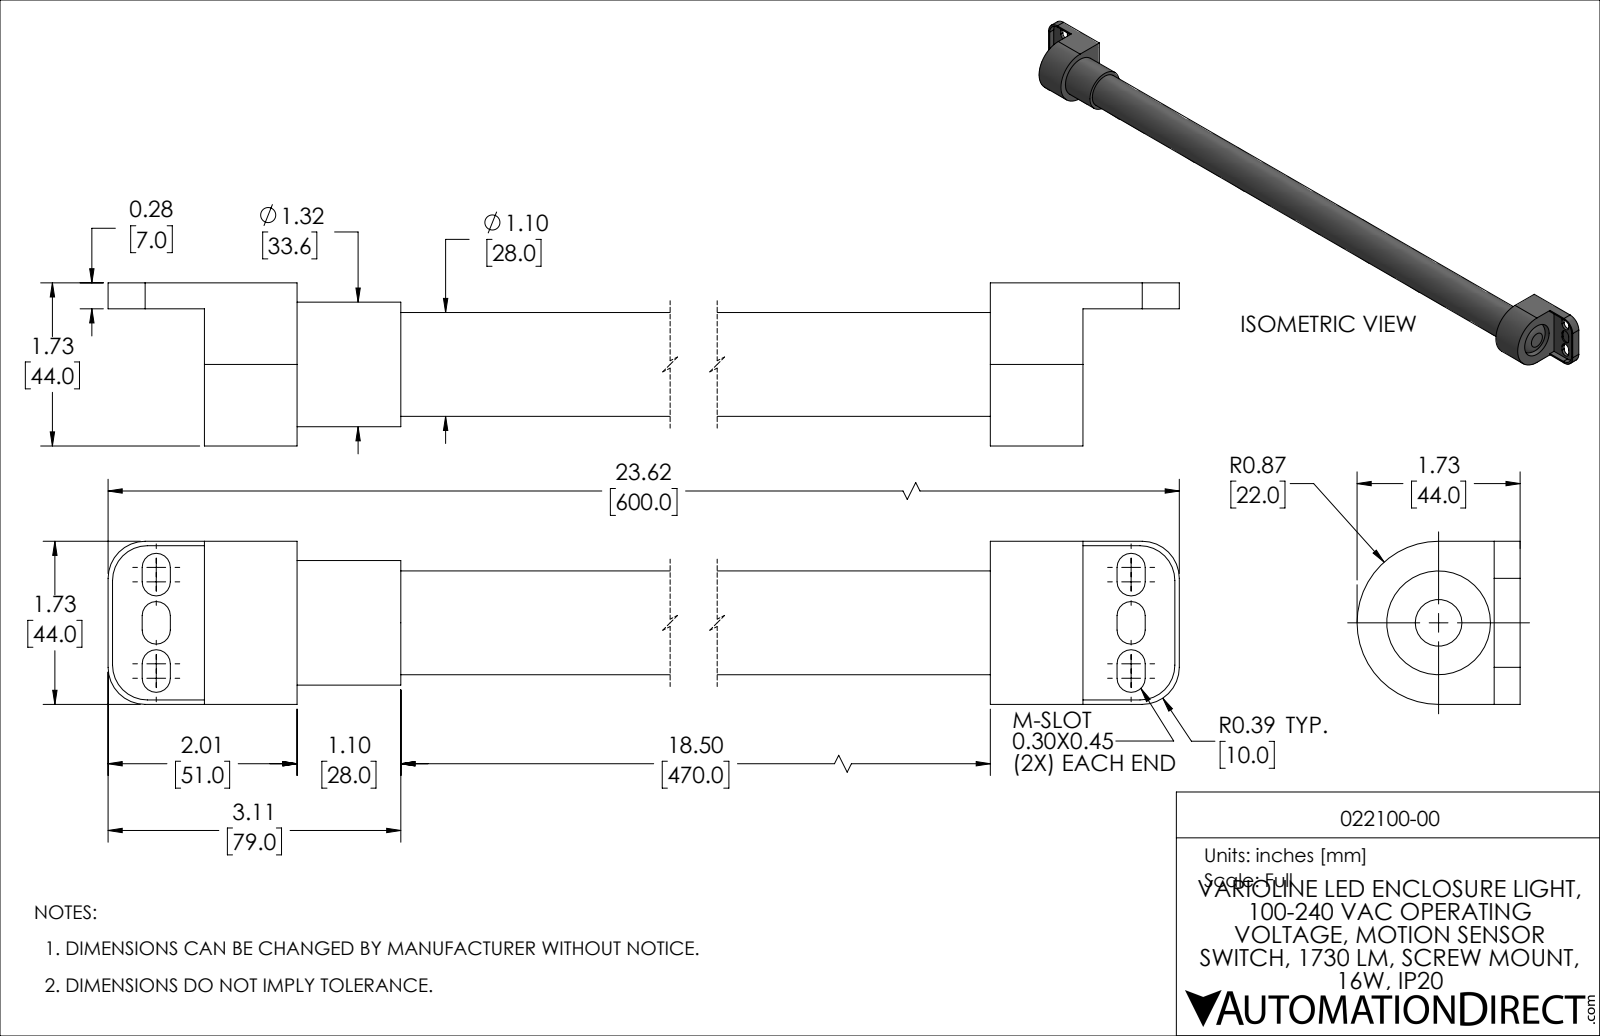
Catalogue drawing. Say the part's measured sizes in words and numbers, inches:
The part is named "PRODUCT_NAME_1". Its 3-D file was written by "ACIS (AUTOMOTIVE_DESIGN_CC2)". It is 1 solid with 73 faces: 39 planar, 30 cylindrical and 4 other. Overall it measures 23.622 by 1.732 by 1.732 inches. Its volume is 24.66 cubic inches and its surface area 102.1 square inches. Round holes: 1 of diameter 1.102. Round bosses or shafts: 1 of diameter 1.323. Partial cylindrical surfaces (rounded edges, fillets, slot ends): 12 of radius 0.15, 4 of radius 0.37, 4 of radius 0.394, 1 of radius 0.866. The main face-to-face distances are 0.984, 20.591, 0.094, 1.732, 21.575, 19.606, 0.047, 22.598, 1.024, 2.008.
